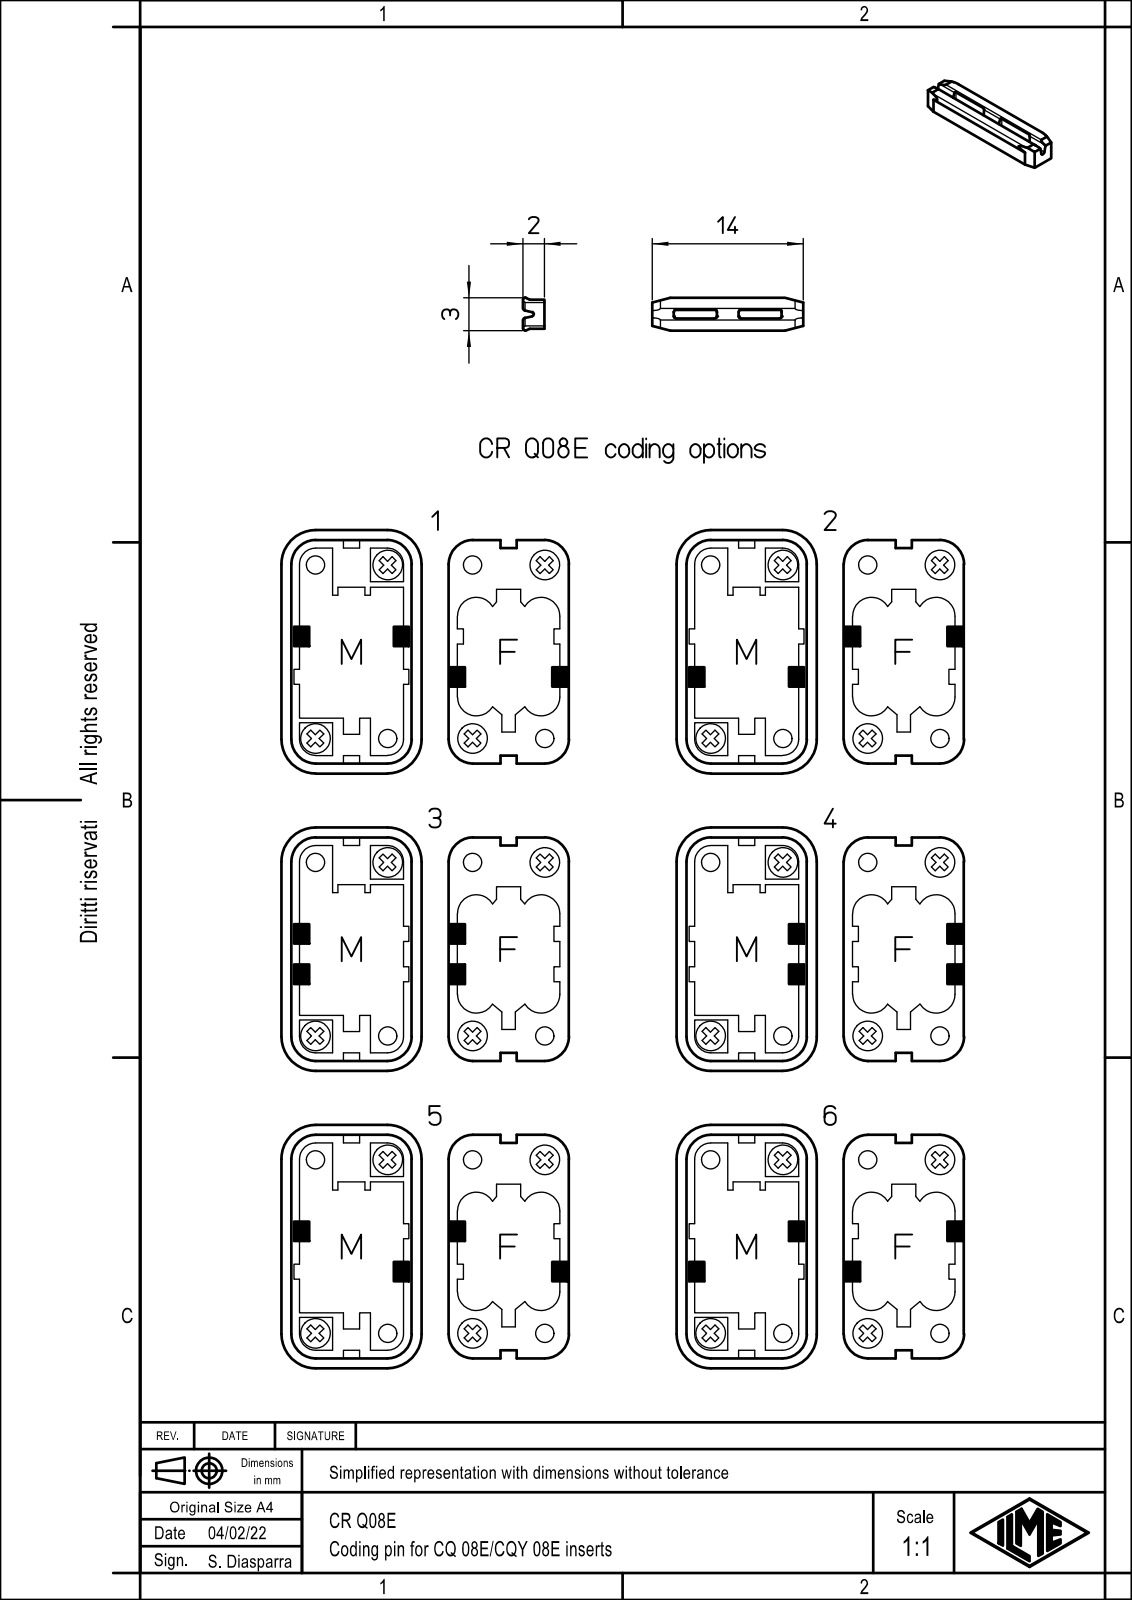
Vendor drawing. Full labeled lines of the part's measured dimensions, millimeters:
Part name (STEP PRODUCT): CR_Q08E
STEP written by: Creo Elements/Direct Modeling 20.1B 02-Apr-2019 (C) Parametric Technology GmbH (AUTOMOTIVE_DESIGN)
Units: millimetres
Bodies: 1 solid, 46 faces (31 planar, 15 cylindrical, 0 other)
Overall size (bounding box): 14 × 3.06 × 2
Volume: 60 mm³ · Surface area: 171 mm²
Partial cylindrical surfaces — rounded edges, fillets, slot ends (radius × count): R0.2 ×13
Main face-to-face distances: 0.95, 1.75, 2, 2.7, 0.8, 5.71, 14, 6, 8, 12
